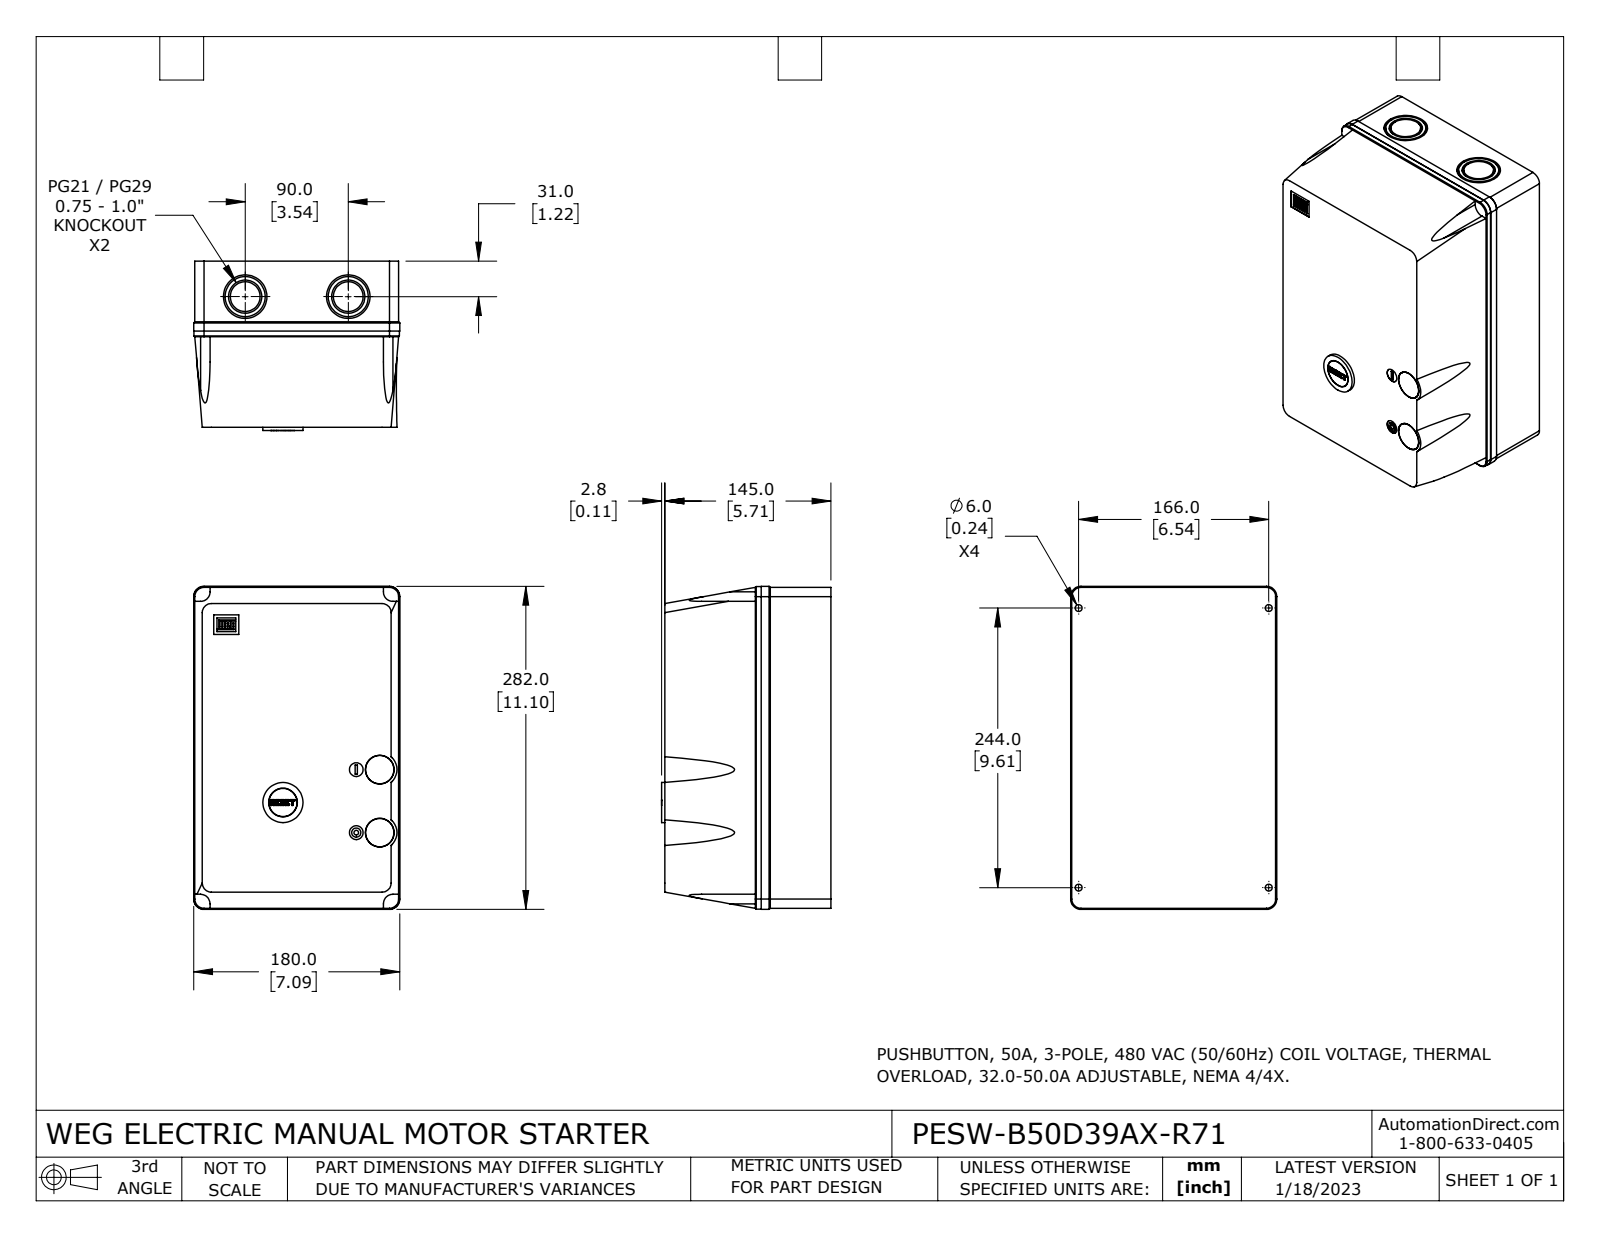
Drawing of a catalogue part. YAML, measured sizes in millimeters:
part_name: "PESW-B50D39AX-R71"
step_written_by: "SolidWorks 2021 (CONFIG_CONTROL_DESIGN)"
units: millimeters
bodies: {solids: 3, faces: 286, planar: 130, cylindrical: 144, other: 12}
overall_size: [282, 180, 147.9]
volume: 7014000
surface_area: 232257
round_holes:
  - {diameter: 6, count: 4}
  - {diameter: 25, count: 3}
  - {diameter: 12, count: 2}
  - {diameter: 29, count: 2}
  - {diameter: 38, count: 2}
  - {diameter: 4, count: 1}
  - {diameter: 30.5, count: 1}
round_bosses_or_shafts:
  - {diameter: 35, count: 3}
  - {diameter: 26, count: 2}
  - {diameter: 24.8, count: 2}
  - {diameter: 30.3, count: 1}
  - {diameter: 24.6, count: 1}
  - {diameter: 14, count: 1}
  - {diameter: 8, count: 1}
partial_cylinders:
  - {radius: 0.1, count: 34}
  - {radius: 8, count: 4}
  - {radius: 8.3, count: 4}
  - {radius: 8.7, count: 4}
  - {radius: 9, count: 4}
  - {radius: 1.6, count: 1}
face_to_face_distances: [145, 178, 280, 1, 0.7, 179, 179.7, 178.7, 281, 180]
hole_center_spacings: [20.5, 55, 58.7, 166, 244, 295.11, 49.14, 57.14]
